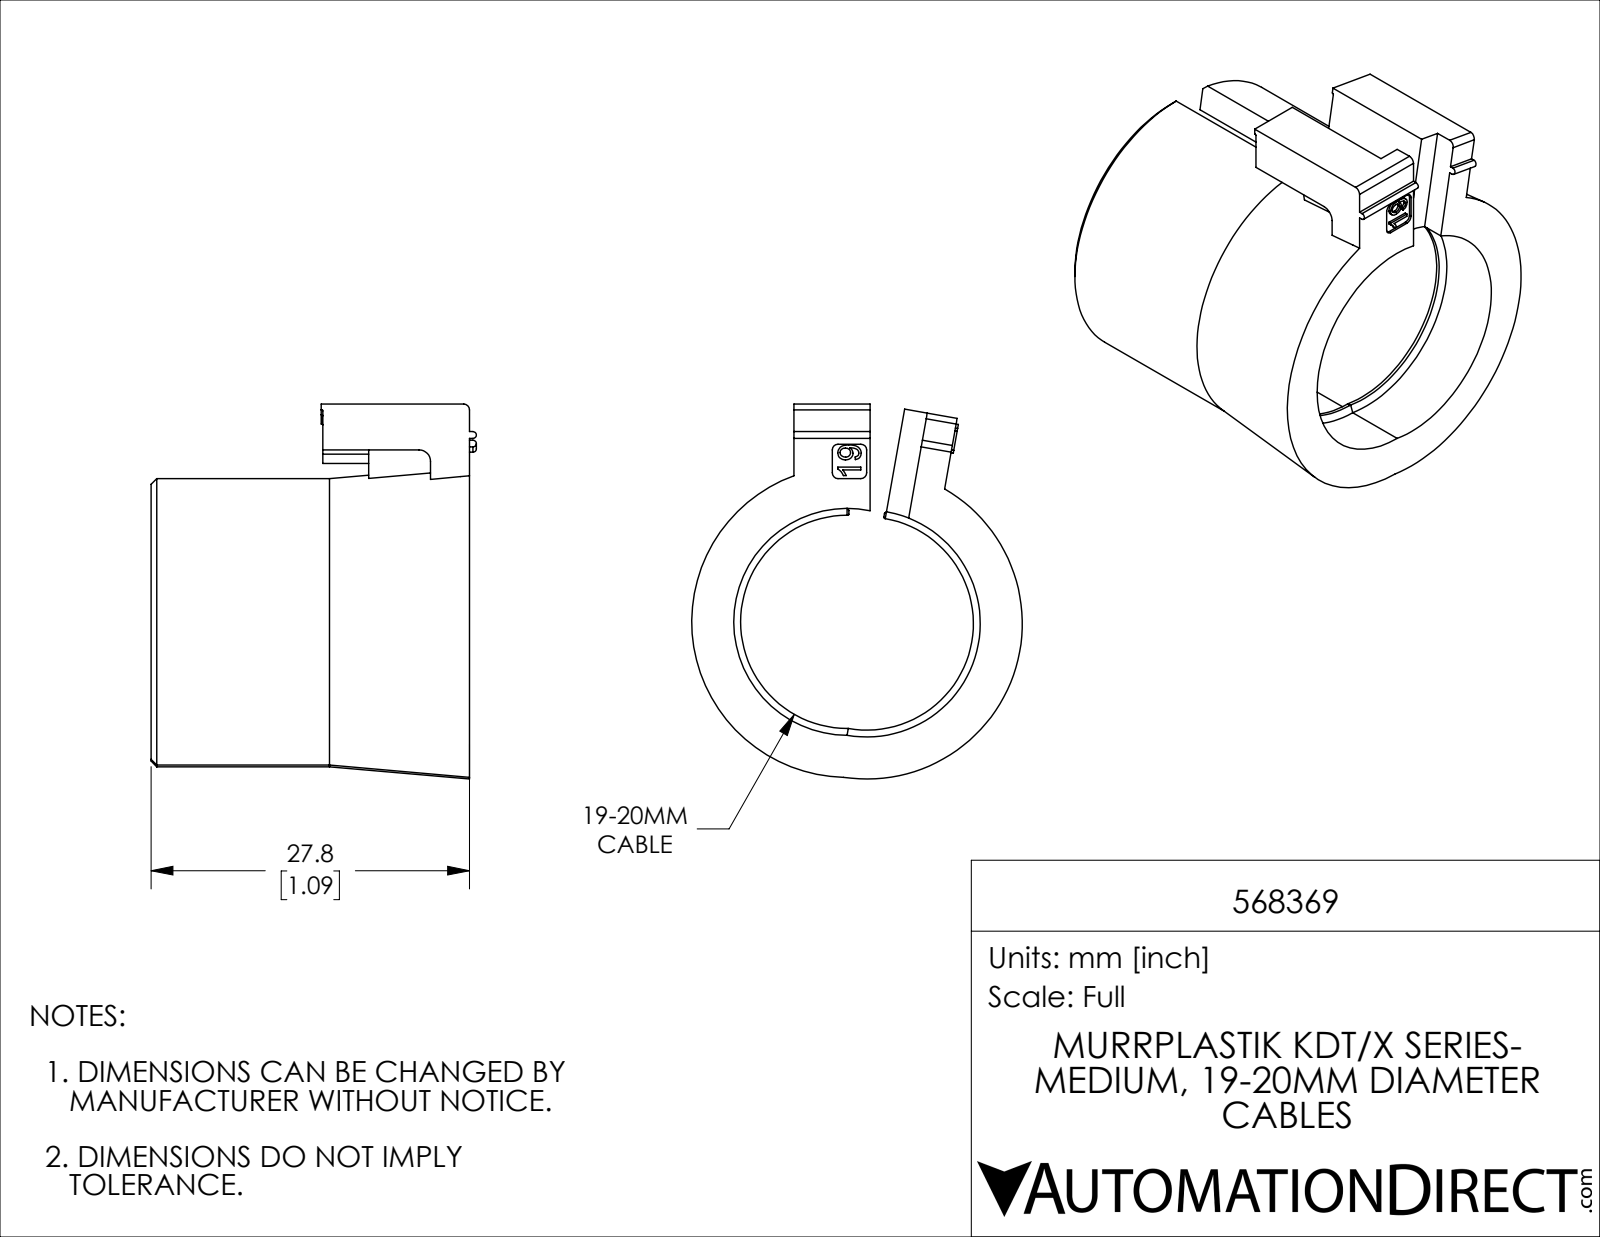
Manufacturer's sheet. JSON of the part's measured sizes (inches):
{"part_name": "568369", "step_written_by": "SolidWorks 2019 (CONFIG_CONTROL_DESIGN)", "units": "inches", "bodies": {"solids": 1, "faces": 125, "planar": 69, "cylindrical": 29, "other": 27}, "overall_size": [1.288, 1.136, 1.118], "volume_in3": 0.379, "surface_area_in2": 7.944, "partial_cylinders_radius": [[0.004, 6], [0.02, 6], [0.012, 2], [0.039, 2], [0.366, 2], [0.39, 2], [0.492, 2]], "face_to_face_distances": [1.094, 0.183, 0.079, 0.157, 1.016, 0.504, 0.425, 0.591, 0.158, 0.262]}
